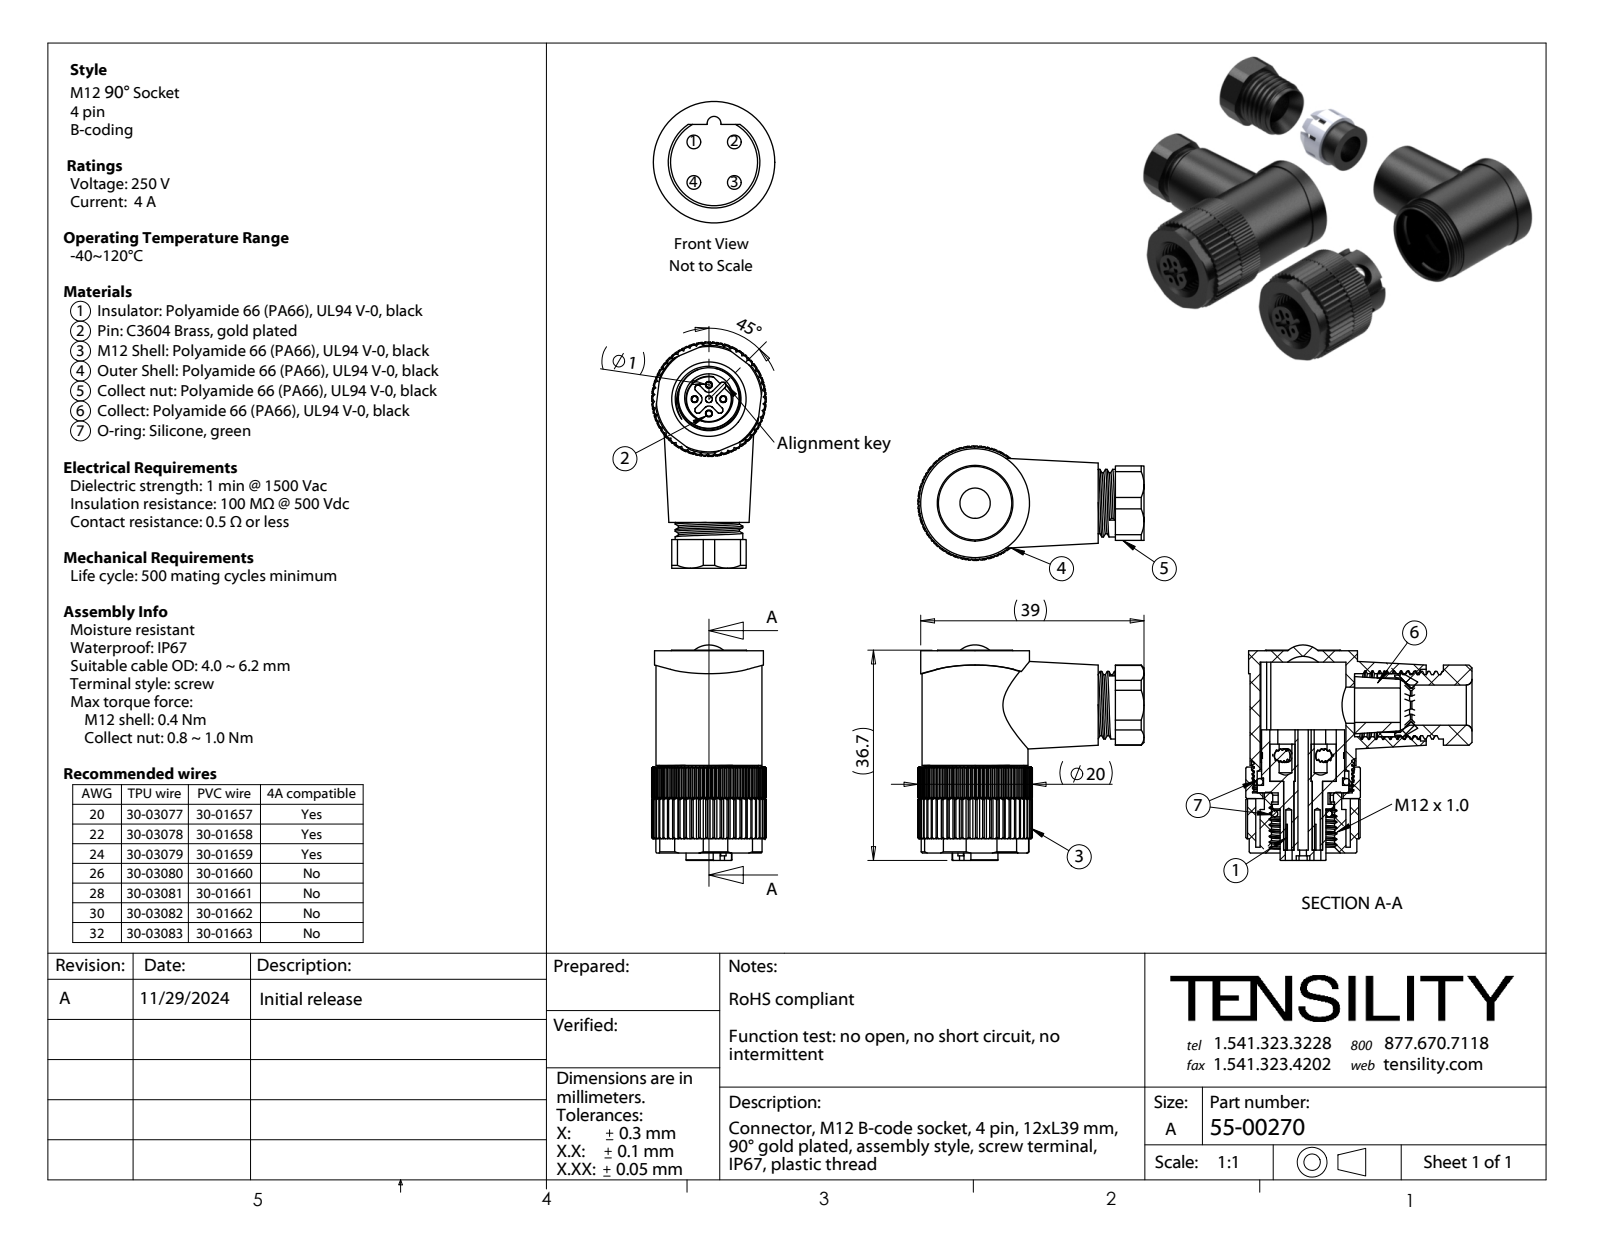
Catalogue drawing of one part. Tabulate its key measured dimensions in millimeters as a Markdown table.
| quantity | value |
| --- | --- |
| part name | 55-00270-01; 55-00270-04; 55-00270-06; 55-00270-03 (+7 more) |
| STEP written by | SolidWorks 2021 (CONFIG_CONTROL_DESIGN) |
| units | millimeters |
| bodies | 16 solids, 1449 faces (522 planar, 485 cylindrical, 442 other) |
| overall size | 39.5 × 37.6 × 20 |
| volume | 8 748 mm³ |
| surface area | 13 869 mm² |
| round holes (diameter × count) | 2.5 × 8, 1.2 × 5, 1.8 × 5, 1 × 4, 2.05 × 4, 5 × 4, 11 × 2, 6 × 1, 6.3 × 1, 7 × 1, 9.5 × 1, 10.6 × 1 |
| round bosses / shafts (diameter × count) | 3.5 × 4, 2.4 × 4, 19 × 1, 18.5 × 1, 17.8 × 1, 17.03 × 1, 17 × 1, 14.5 × 1 |
| partial cylindrical surfaces (radius × count) | 0.55 × 4, 1 × 4, 1.75 × 4, 6.45 × 1, 6.5 × 1, 7 × 1, 9.4 × 1, 10 × 1 |
| main face-to-face distances | 1, 2, 22.8, 24.8, 25.8, 9.5, 11.8, 12.5, 13.44, 13.8 |
| hole center spacings | 5.14, 5.13, 0.8, 2.5, 3.12, 3.54, 3.62, 4.34 |
